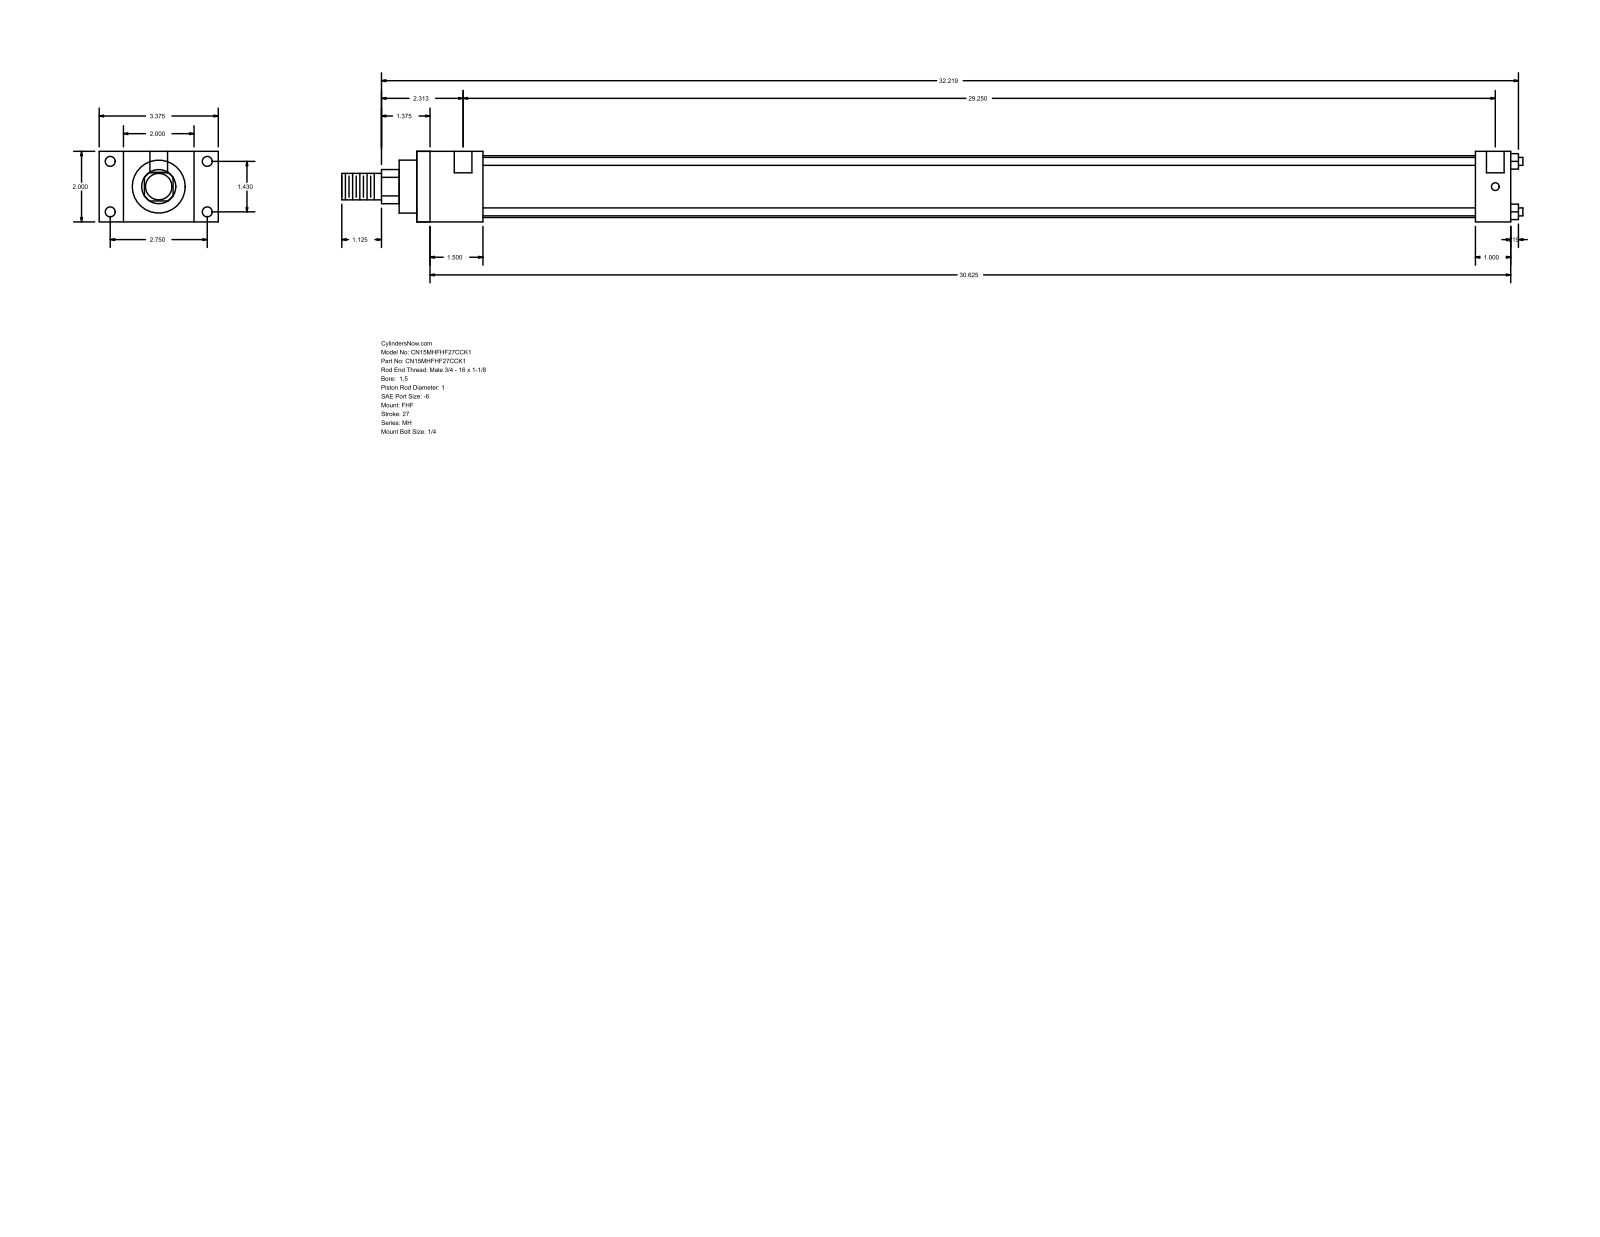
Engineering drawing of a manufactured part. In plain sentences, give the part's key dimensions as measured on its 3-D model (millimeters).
The part is named "MH_FHF__0150_1". Its 3-D file was written by "GSSL Pune (CONFIG_CONTROL_DESIGN)". It is 0 solids with 88 faces: 60 planar, 28 cylindrical and 0 other. Overall it measures 850.11 by 85.72 by 50.8 millimeters. Round holes: 4 of diameter 5.56, 4 of diameter 7.14, 2 of diameter 12.7. Round bosses or shafts: 4 of diameter 5.71, 1 of diameter 44.45, 1 of diameter 38.1, 1 of diameter 25.4, 1 of diameter 19.05. Partial cylindrical surfaces (rounded edges, fillets, slot ends): 1 of radius 12.29. The main face-to-face distances are 50.8, 17.46, 68.26, 47.63, 85.72, 787.4, 739.77, 25.4, 762, 714.37. The hole center spacings are 36.32, 69.84, 78.72, 746.13, 3.18, 742.95.
